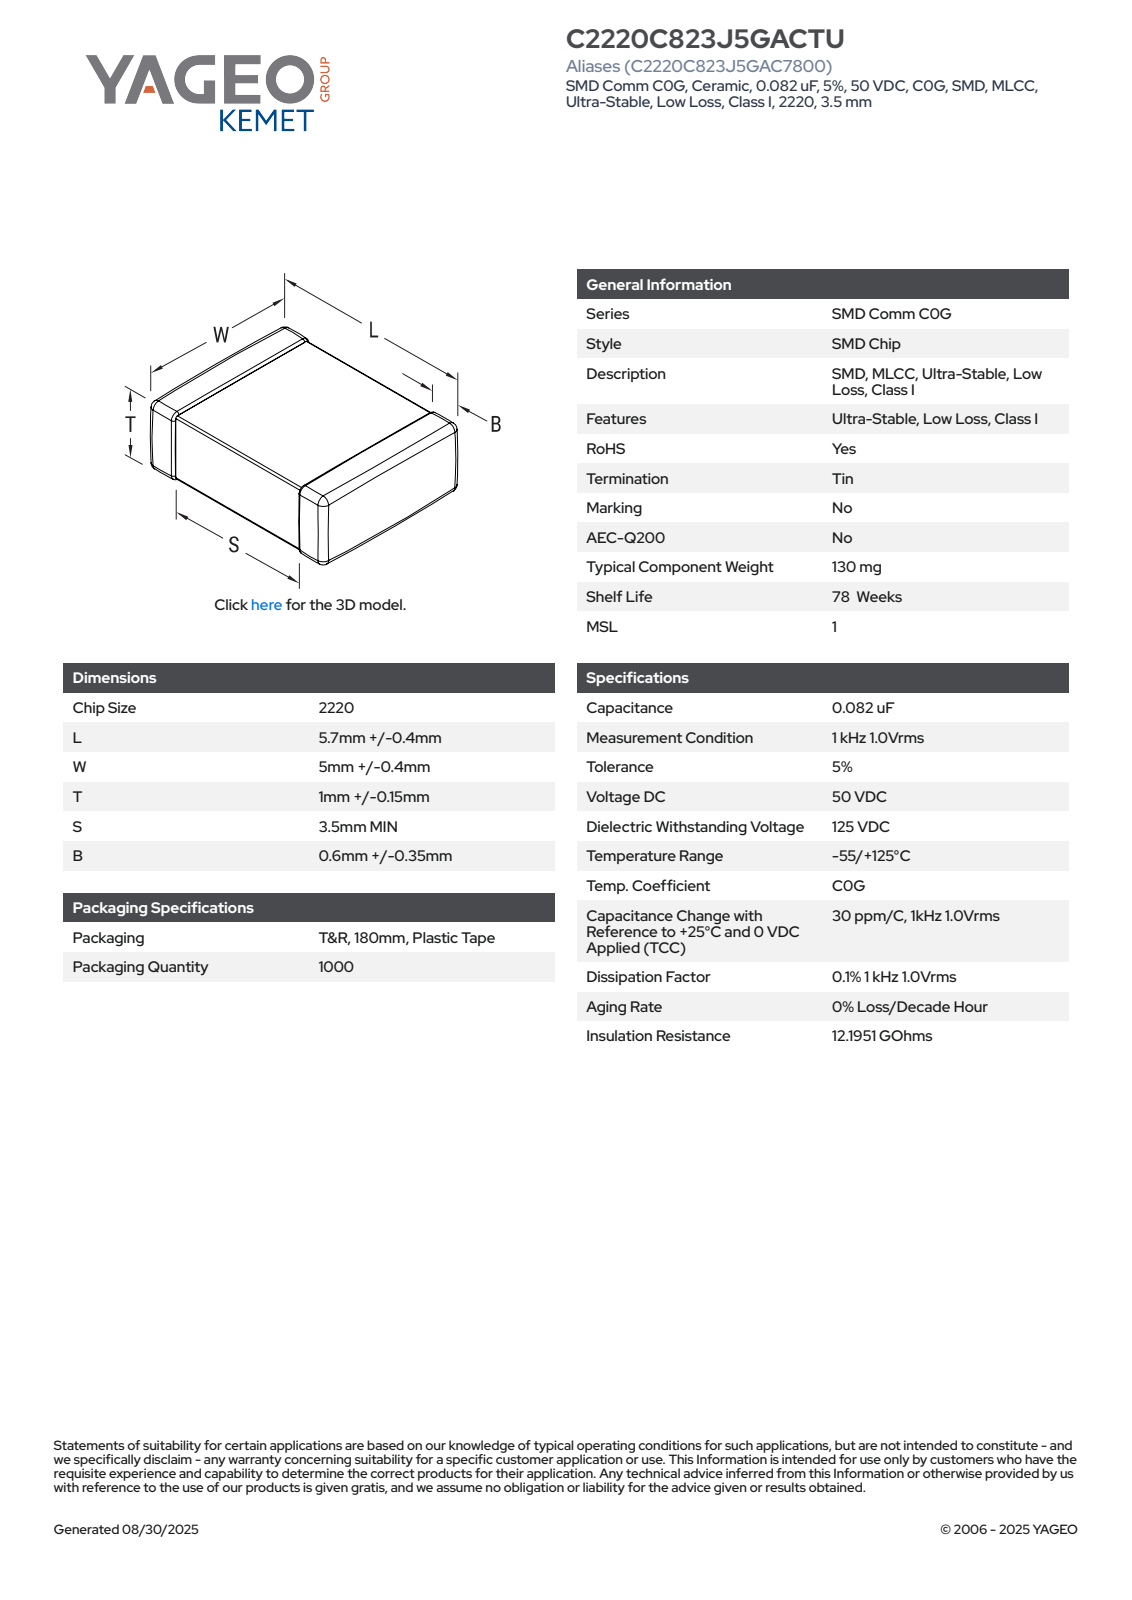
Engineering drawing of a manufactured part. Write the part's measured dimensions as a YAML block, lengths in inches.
part_name: "CCS_CCSTD_2220_L6.1W5.4T1.15B0.6"
step_written_by: "SolidWorks 2021 (AUTOMOTIVE_DESIGN)"
units: inches
bodies: {solids: 4, faces: 125, planar: 71, cylindrical: 38, other: 16}
overall_size: [0.24, 0.213, 0.045]
volume: 0.002
surface_area: 0.14
partial_cylinders:
  - {radius: 0.004, count: 24}
face_to_face_distances: [0.037, 0.041, 0.045, 0.24, 0.204, 0.208, 0.213, 0.098, 0.142, 0.13]
